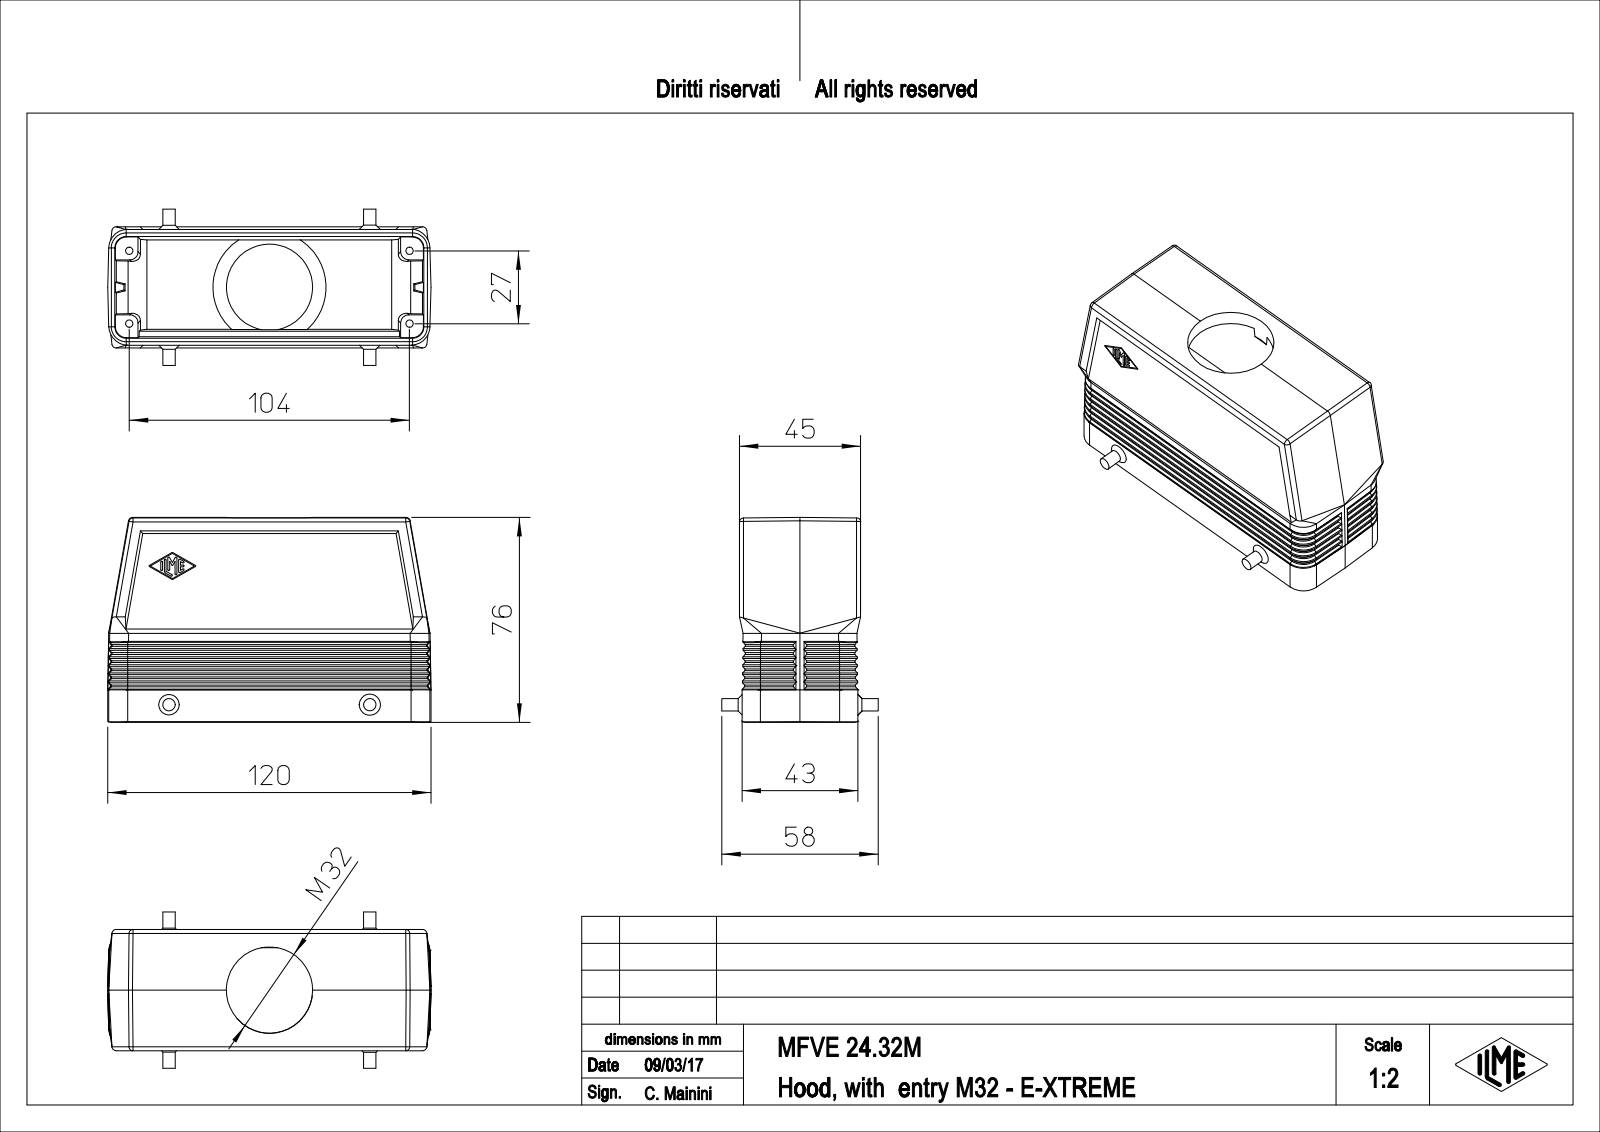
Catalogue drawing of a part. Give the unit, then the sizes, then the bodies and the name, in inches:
Units: inches
Overall size (bounding box): 4.724 × 2.992 × 2.283
Round holes (diameter × count): ⌀0.108 ×4, ⌀1.26 ×1
Round bosses / shafts (diameter × count): ⌀0.181 ×2
Partial cylindrical surfaces — rounded edges, fillets, slot ends (radius × count): R0.02 ×78, R0.059 ×10, R0.276 ×8, R0.118 ×4, R0.165 ×4, R0.827 ×1
Main face-to-face distances: 1.693, 0.079, 0.079, 0.157, 0.039, 1.732, 0.333, 0.236, 0.237, 0.158
Hole centre spacings: 2.115, 1.063, 4.094, 4.23
Volume: 6.493 in³ · Surface area: 83.56 in²
Bodies: 1 solid, 476 faces (208 planar, 132 cylindrical, 136 other)
Part name (STEP PRODUCT): MFVE_24.32M
STEP written by: PTC Creo Elements/Direct Modeling 19.0E 27-Jun-2016 (C) Parametric Technology GmbH (AUTOMOTIVE_DESIGN)
